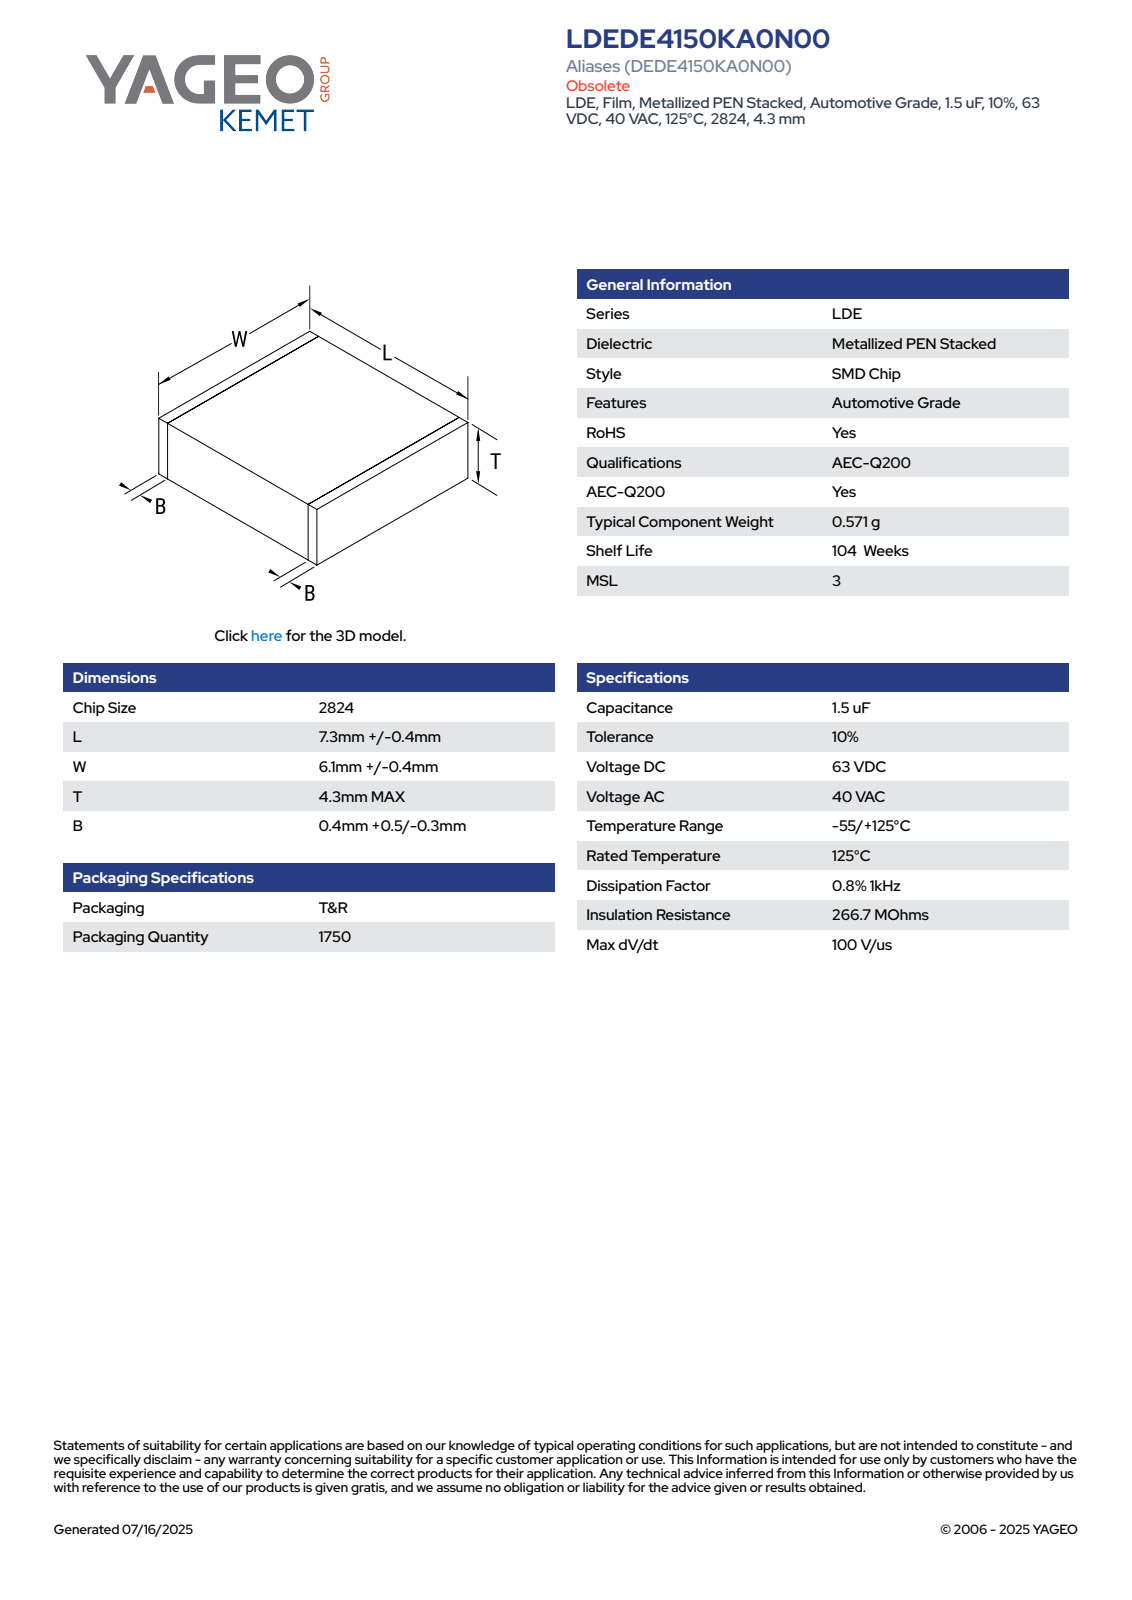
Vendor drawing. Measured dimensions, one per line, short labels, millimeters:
name: CFS_LDELDB_2824_L7.7W6.5T4.3B0.9
written by: SolidWorks 2020 (AUTOMOTIVE_DESIGN)
unit: mm
bodies: 4 solids, 73 faces (73 planar, 0 cylindrical, 0 other)
size: 7.7 × 6.5 × 4.3
volume: 214 mm³; area: 225 mm²
face distances: 4.28, 6.48, 7.7, 4.29, 6.49, 4.3, 6.5, 0.5, 7.2, 6.7
